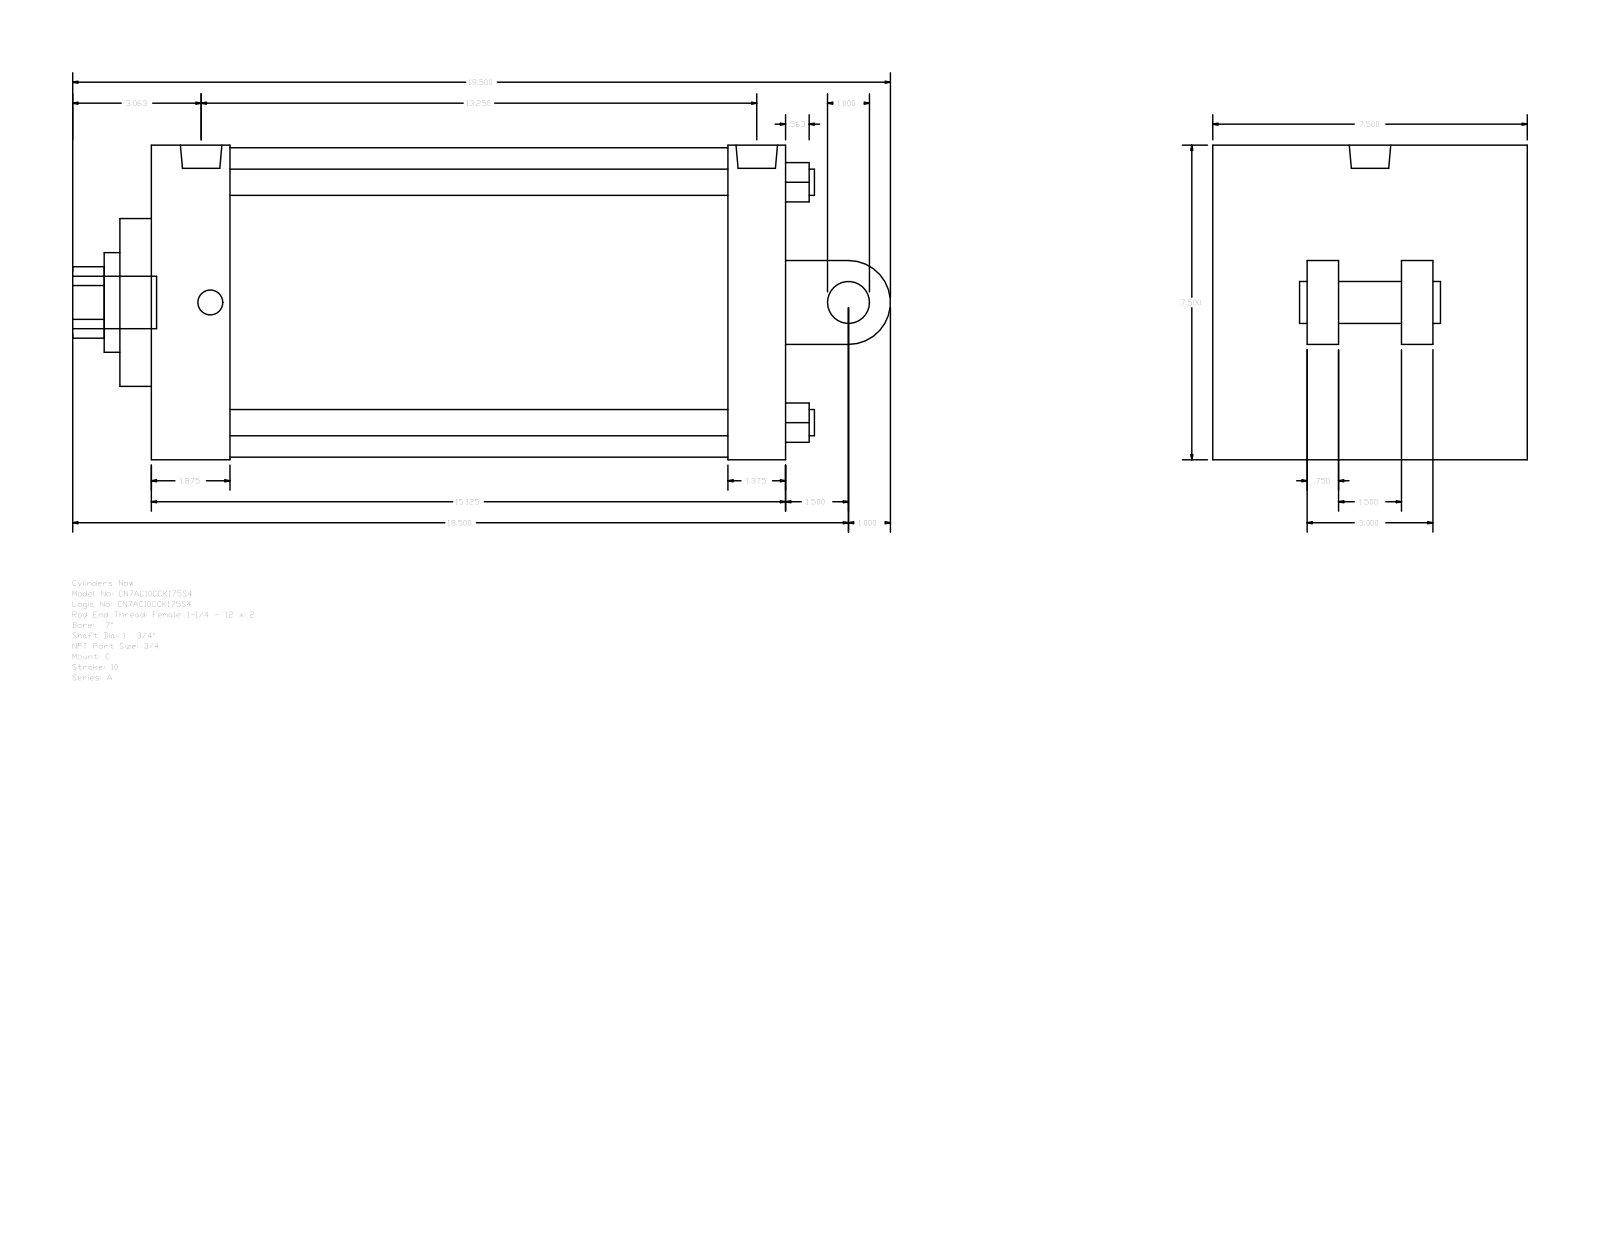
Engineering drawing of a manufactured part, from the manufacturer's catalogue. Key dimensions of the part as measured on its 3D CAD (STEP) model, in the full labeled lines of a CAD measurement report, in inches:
Part name (STEP PRODUCT): A_C__0700_1.75
STEP written by: GSSL Pune (CONFIG_CONTROL_DESIGN)
Units: inches
Bodies: 0 solids, 104 faces (75 planar, 29 cylindrical, 0 other)
Overall size (bounding box): 19.5 × 7.5 × 7.5
Round holes (diameter × count): ⌀0.625 ×4, ⌀0.594 ×2, ⌀0.989 ×1, ⌀1.75 ×1, ⌀2.375 ×1, ⌀7.375 ×1
Round bosses / shafts (diameter × count): ⌀0.594 ×2, ⌀1.25 ×1, ⌀1 ×1, ⌀0.989 ×1
Partial cylindrical surfaces — rounded edges, fillets, slot ends (radius × count): R0.852 ×1, R1 ×1
Main face-to-face distances: 7.5, 15.125, 0.75, 3, 2.25, 1.75, 1.375, 1.875, 13.25, 13.75
Hole centre spacings: 4.052, 5.73, 8.103, 0.219
